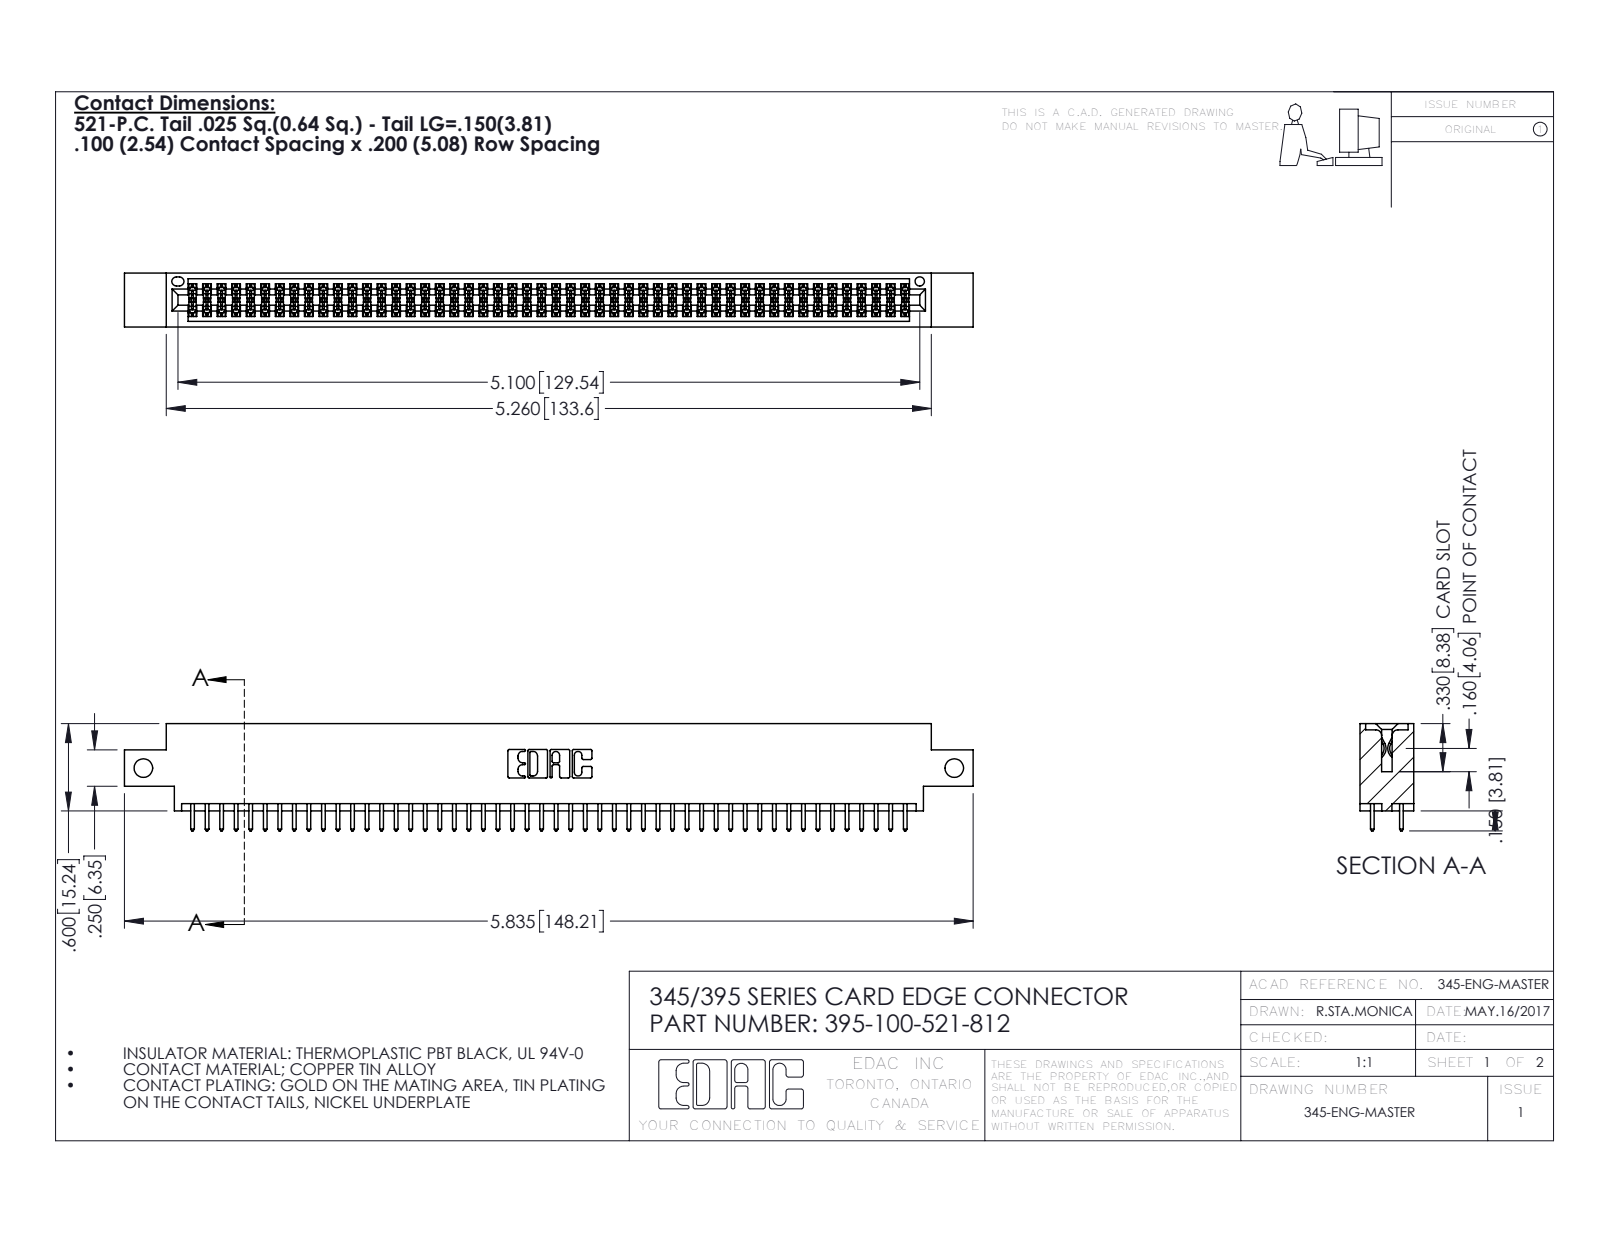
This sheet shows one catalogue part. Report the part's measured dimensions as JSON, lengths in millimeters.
{"part_name": "395-100-521-812; 345 Part_0.170 Offset - Side Mount; 345-292-001_345-293-121", "step_written_by": "SolidWorks 2016 (CONFIG_CONTROL_DESIGN)", "units": "millimeters", "bodies": {"solids": 101, "faces": 5130, "planar": 3384, "cylindrical": 1746, "other": 0}, "overall_size": [148.2, 18.7, 9.4], "volume_mm3": 14200, "surface_area_mm2": 20930, "round_holes": [[3.3, 2], [1.6, 1]], "partial_cylinders_radius": [[0.2, 150], [0.3, 100], [0.3, 22], [0.2, 6], [0.8, 6], [0.7, 3], [0.4, 2], [0.5, 2]], "face_to_face_distances": [7.6, 1.8, 9.4, 5.1, 2.5, 6.9, 0.6, 5.7, 4.4, 3.8], "hole_center_spacings": [141.6]}
